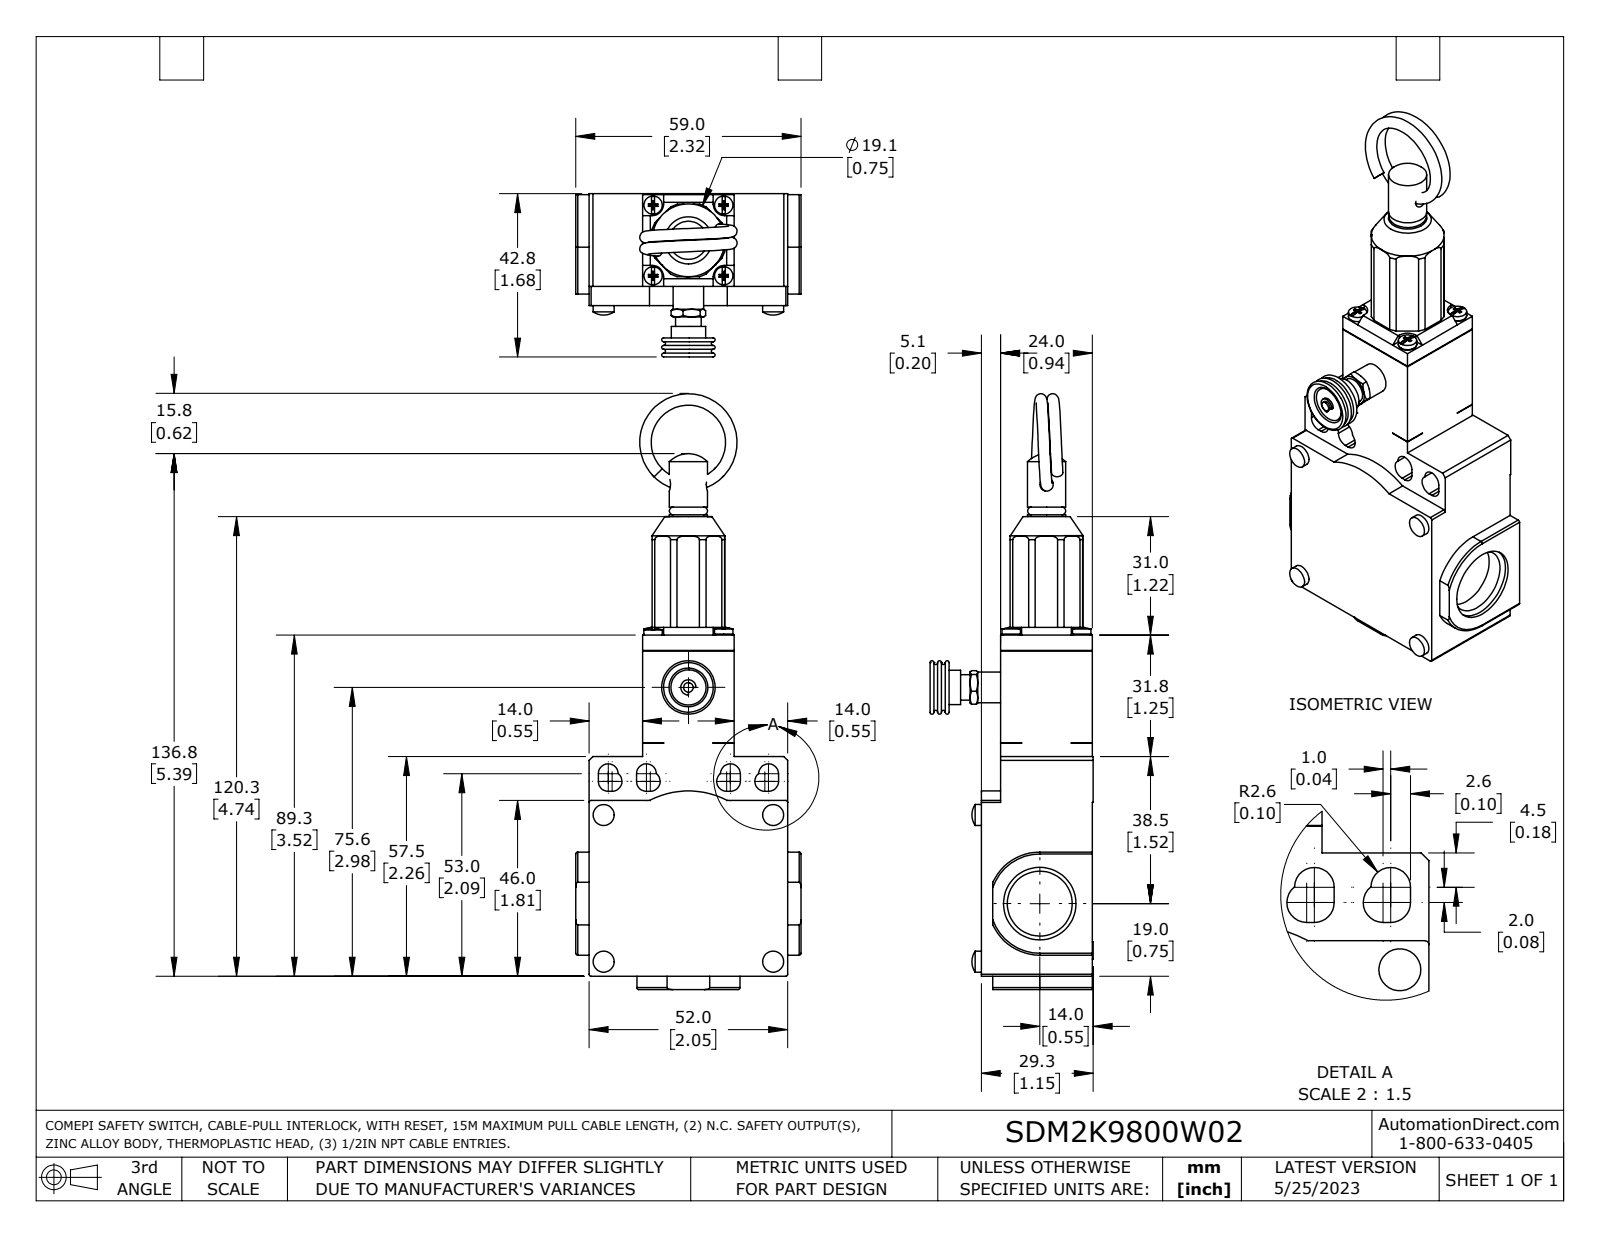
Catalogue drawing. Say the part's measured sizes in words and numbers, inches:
The part is named "SDM2K9800W02". Its 3-D file was written by "SolidWorks 2021 (AUTOMOTIVE_DESIGN)". It is 5 solids with 344 faces: 212 planar, 85 cylindrical and 47 other. Overall it measures 6.141 by 2.323 by 1.683 inches. Its volume is 6.887 cubic inches and its surface area 42.73 square inches. Round holes: 4 of diameter 0.118, 2 of diameter 0.669, 2 of diameter 0.748, 1 of diameter 0.138, 1 of diameter 0.157, 1 of diameter 0.236, 1 of diameter 0.276. Round bosses or shafts: 4 of diameter 0.217, 4 of diameter 0.189, 1 of diameter 0.394, 1 of diameter 0.354, 1 of diameter 0.315, 1 of diameter 0.264, 1 of diameter 0.248, 1 of diameter 0.187. Partial cylindrical surfaces (rounded edges, fillets, slot ends): 12 of radius 0.102, 10 of radius 0.02, 9 of radius 0.039, 4 of radius 0.118, 2 of radius 0.531, 1 of radius 0.4, 1 of radius 0.866. The main face-to-face distances are 1.144, 0.945, 0.551, 1.496, 0.138, 0.199, 2.047, 0.236, 2.185, 0.098. The hole center spacings are 0.728, 0.469, 0.566, 1.03, 4.321.
